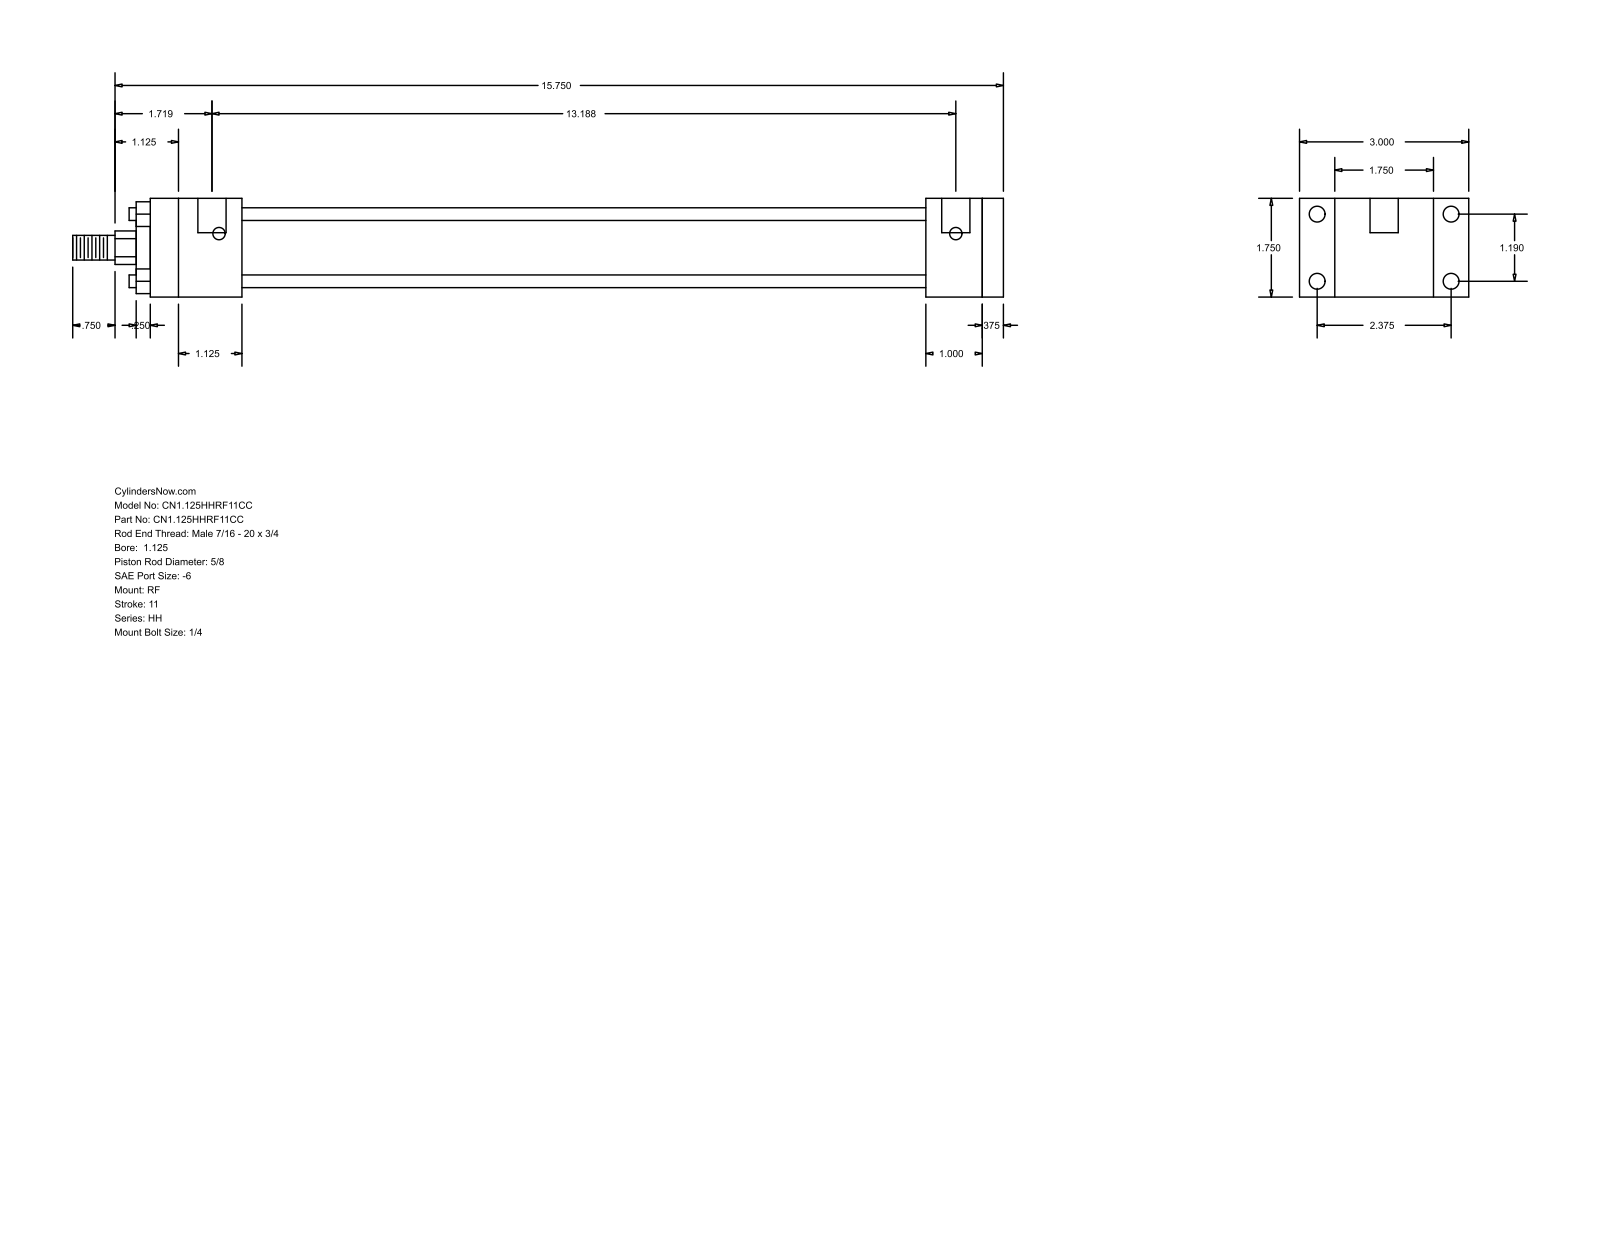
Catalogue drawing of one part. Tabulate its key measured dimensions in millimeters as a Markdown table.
| quantity | value |
| --- | --- |
| part name | HH_RF__0112_0.625 |
| STEP written by | GSSL Pune (CONFIG_CONTROL_DESIGN) |
| units | millimeters |
| bodies | 0 solids, 92 faces (64 planar, 28 cylindrical, 0 other) |
| overall size | 419.1 × 76.2 × 44.45 |
| round holes (diameter × count) | 5.56 × 4, 7.14 × 4, 12.7 × 2 |
| round bosses / shafts (diameter × count) | 5.71 × 4, 34.92 × 1, 28.57 × 1, 15.88 × 1, 11.11 × 1 |
| partial cylindrical surfaces (radius × count) | 7.54 × 1 |
| main face-to-face distances | 44.46, 9.53, 384.17, 25.4, 34.93, 15.87, 333.37, 342.9, 307.97, 41.27 |
| hole center spacings | 30.22, 60.32, 67.47, 331.79, 3.17, 334.96 |
